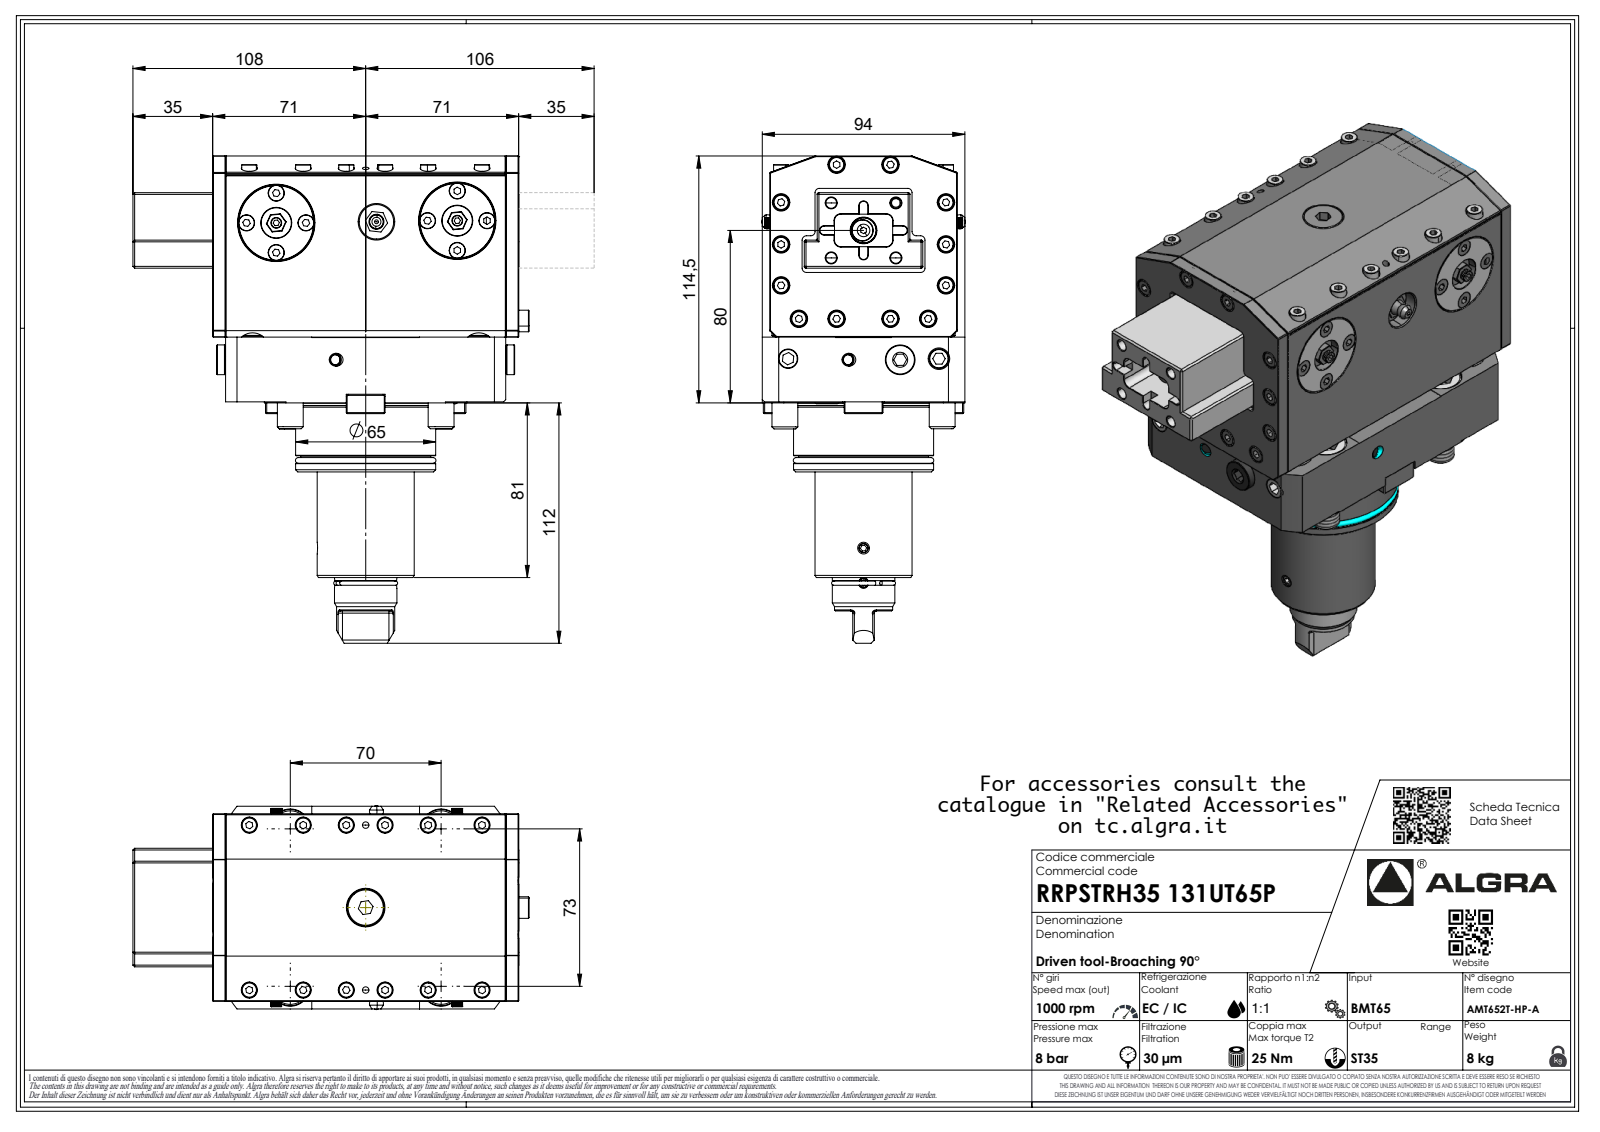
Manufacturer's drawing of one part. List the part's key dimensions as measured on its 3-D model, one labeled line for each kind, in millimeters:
Part name (STEP PRODUCT): RRPSTRH35131UT65P
STEP written by: SolidWorks 2023 (AUTOMOTIVE_DESIGN)
Units: millimetres
Bodies: 1 solid, 882 faces (482 planar, 151 cylindrical, 249 other)
Overall size (bounding box): 226 × 183.82 × 94.6
Volume: 1 645 000 mm³ · Surface area: 102 501 mm²
Round holes (diameter × count): ⌀2.1 ×1, ⌀5.5 ×1, ⌀6 ×1
Round bosses / shafts (diameter × count): ⌀7 ×12, ⌀5 ×2, ⌀65 ×1, ⌀64.6 ×1, ⌀60.3 ×1, ⌀45 ×1, ⌀29 ×1, ⌀27 ×1
Partial cylindrical surfaces — rounded edges, fillets, slot ends (radius × count): R3 ×12, R0.5 ×8, R0.33 ×7, R0.52 ×7, R3.7 ×7, R1 ×6, R6 ×4, R7.5 ×4
Main face-to-face distances: 87, 3.5, 90.5, 6, 136, 142, 0.5, 114.5, 114, 94
